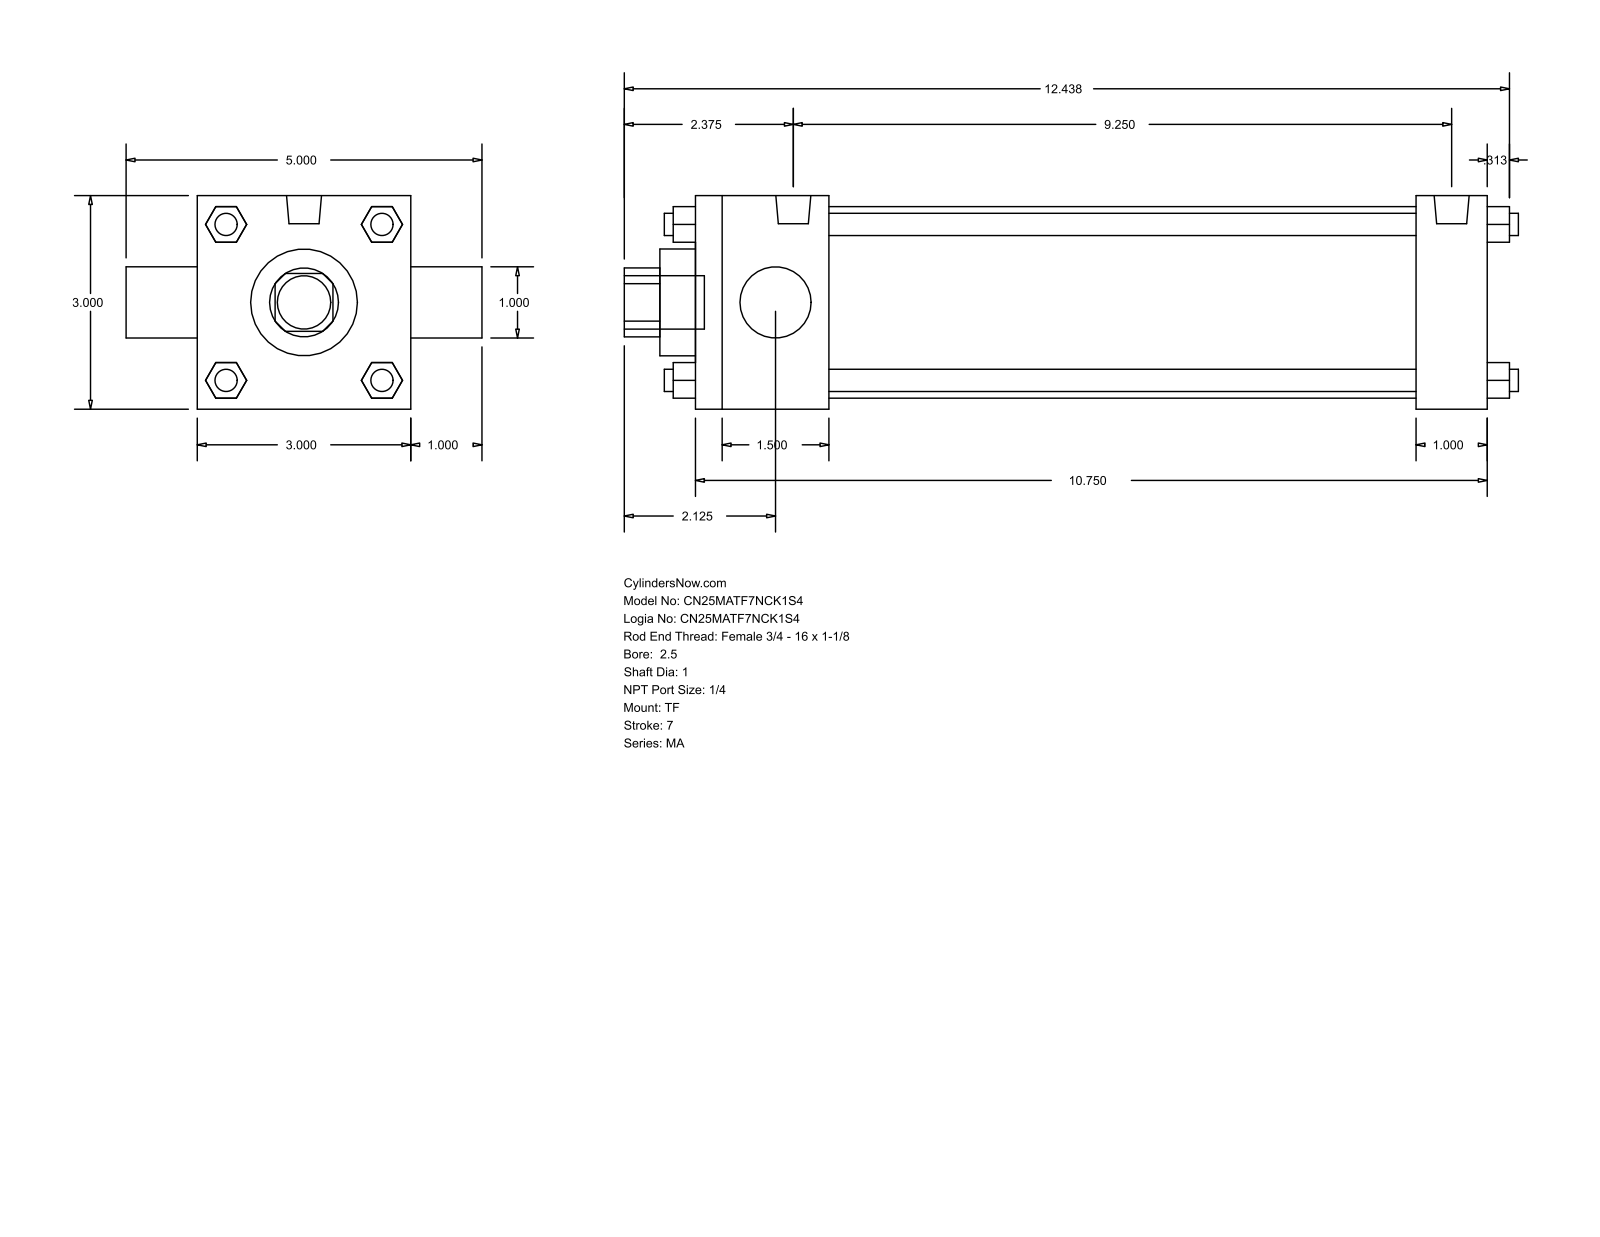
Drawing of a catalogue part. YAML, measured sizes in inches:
part_name: "MA_TF__0250_1"
step_written_by: "GSSL Pune (CONFIG_CONTROL_DESIGN)"
units: inches
bodies: {solids: 0, faces: 120, planar: 92, cylindrical: 28, other: 0}
overall_size: [12.563, 5, 3]
round_holes:
  - {diameter: 1, count: 2}
  - {diameter: 1.5, count: 1}
  - {diameter: 2.69, count: 1}
round_bosses_or_shafts:
  - {diameter: 0.313, count: 7}
  - {diameter: 0.492, count: 2}
  - {diameter: 0.75, count: 1}
partial_cylinders:
  - {radius: 0.484, count: 1}
face_to_face_distances: [3, 11.125, 0.5, 1.875, 10.125, 8.25, 9.25, 1, 1, 4]
